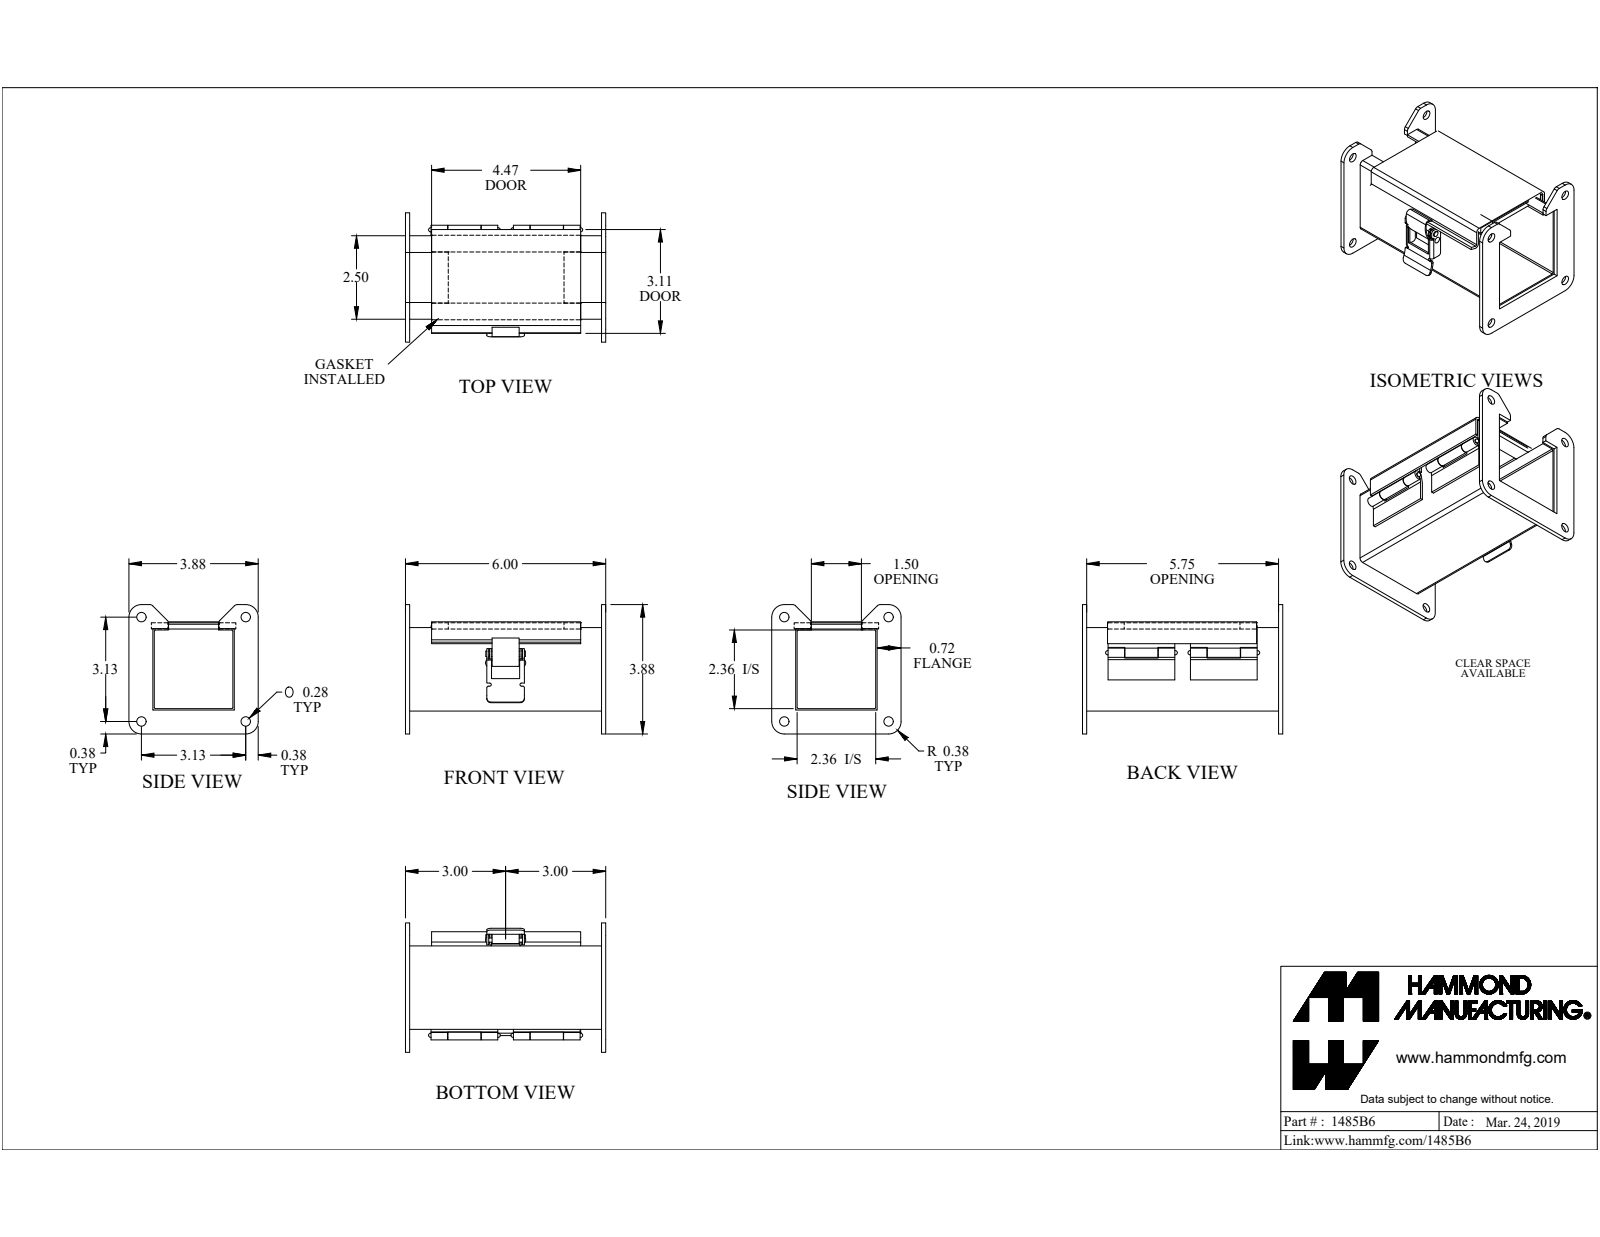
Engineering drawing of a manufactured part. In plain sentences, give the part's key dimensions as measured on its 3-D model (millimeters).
The part is named "1485B6". Its 3-D file was written by "SolidWorks 2019 (CONFIG_CONTROL_DESIGN)". It is 17 solids with 281 faces: 178 planar, 95 cylindrical and 8 other. Overall it measures 152.4 by 98.4 by 98.4 millimeters. Its volume is 139 500 cubic millimeters and its surface area 139 200 square millimeters. Round holes: 4 of diameter 7.1, 1 of diameter 3.2, 1 of diameter 4.2. Round bosses or shafts: 1 of diameter 7, 1 of diameter 4.1, 1 of diameter 4, 1 of diameter 3.2, 1 of diameter 3.2. Partial cylindrical surfaces (rounded edges, fillets, slot ends): 7 of radius 0.9, 7 of radius 2.7, 7 of radius 3.2, 4 of radius 0.7, 4 of radius 2.2, 4 of radius 9.5, 2 of radius 0.4, 2 of radius 1.2. The main face-to-face distances are 1.8, 61.7, 66, 63.5, 59.8, 3.2, 149.2, 67.9, 64.2, 4.4. The hole center spacings are 79.4, 112.3, 27.3, 27.9, 51.5, 52.4, 74.3, 80.6.
